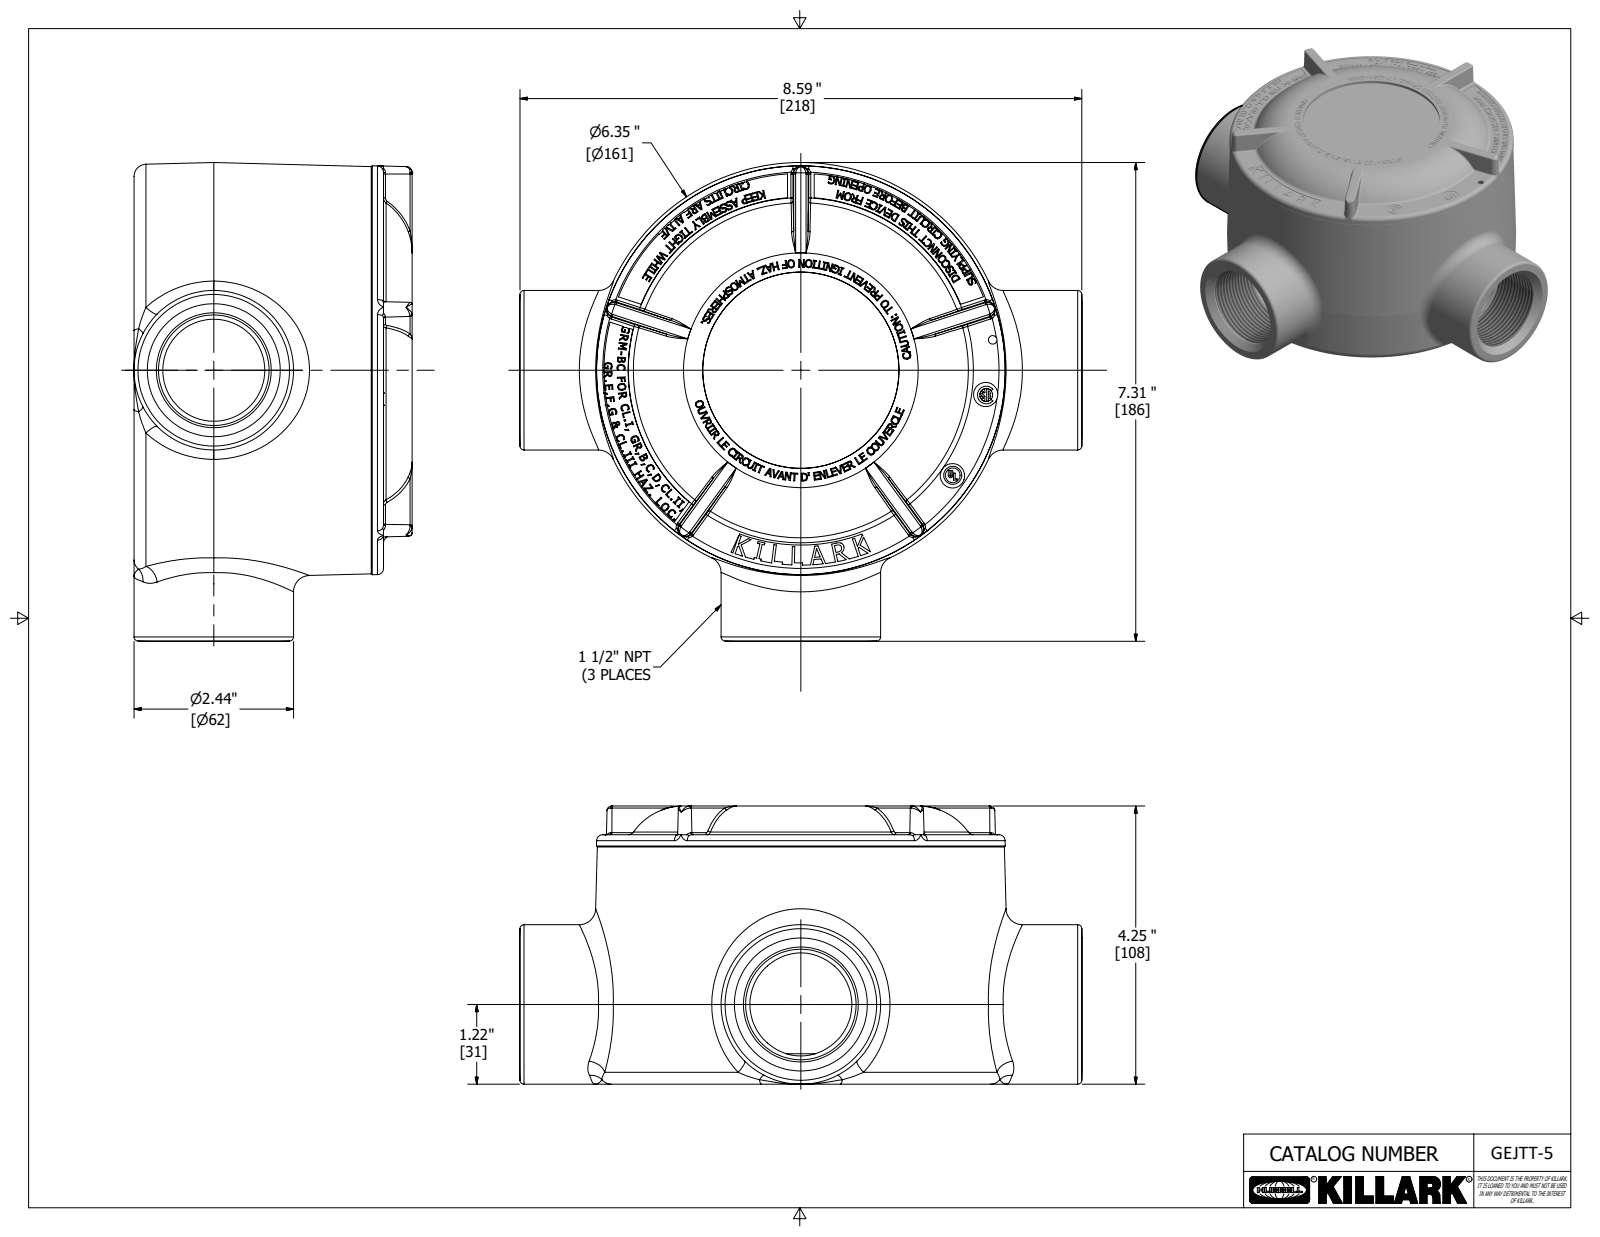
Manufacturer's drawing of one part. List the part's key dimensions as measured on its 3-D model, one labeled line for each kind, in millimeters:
Part name (STEP PRODUCT): GEJTT-5; 0071700M; 17805ABAM; 15722VANB
STEP written by: Autodesk Inventor 2020 (AUTOMOTIVE_DESIGN)
Units: millimetres
Bodies: 3 solids, 5329 faces (2885 planar, 114 cylindrical, 2330 other)
Overall size (bounding box): 218.3 × 185.8 × 108
Volume: 829 800 mm³ · Surface area: 224 500 mm²
Round holes (diameter × count): ⌀3.3 ×1, ⌀5 ×1, ⌀5.7 ×1, ⌀9.4 ×1, ⌀9.4 ×1, ⌀39.6 ×1, ⌀134.2 ×1, ⌀138 ×1, ⌀144.4 ×1
Round bosses / shafts (diameter × count): ⌀61.9 ×2, ⌀136.5 ×1, ⌀7 ×1
Partial cylindrical surfaces — rounded edges, fillets, slot ends (radius × count): R0.8 ×20, R1.6 ×10, R0.2 ×1, R0.9 ×1, R1.8 ×1, R2.5 ×1, R2.5 ×1, R3.4 ×1
Main face-to-face distances: 0.8, 88.9, 8, 89.7, 97.6, 92.1, 5.6, 84.2, 83.3, 8.7
Hole centre spacings: 18.4, 18.5, 21.4, 33.9, 34.1, 44.1, 54.8, 55
